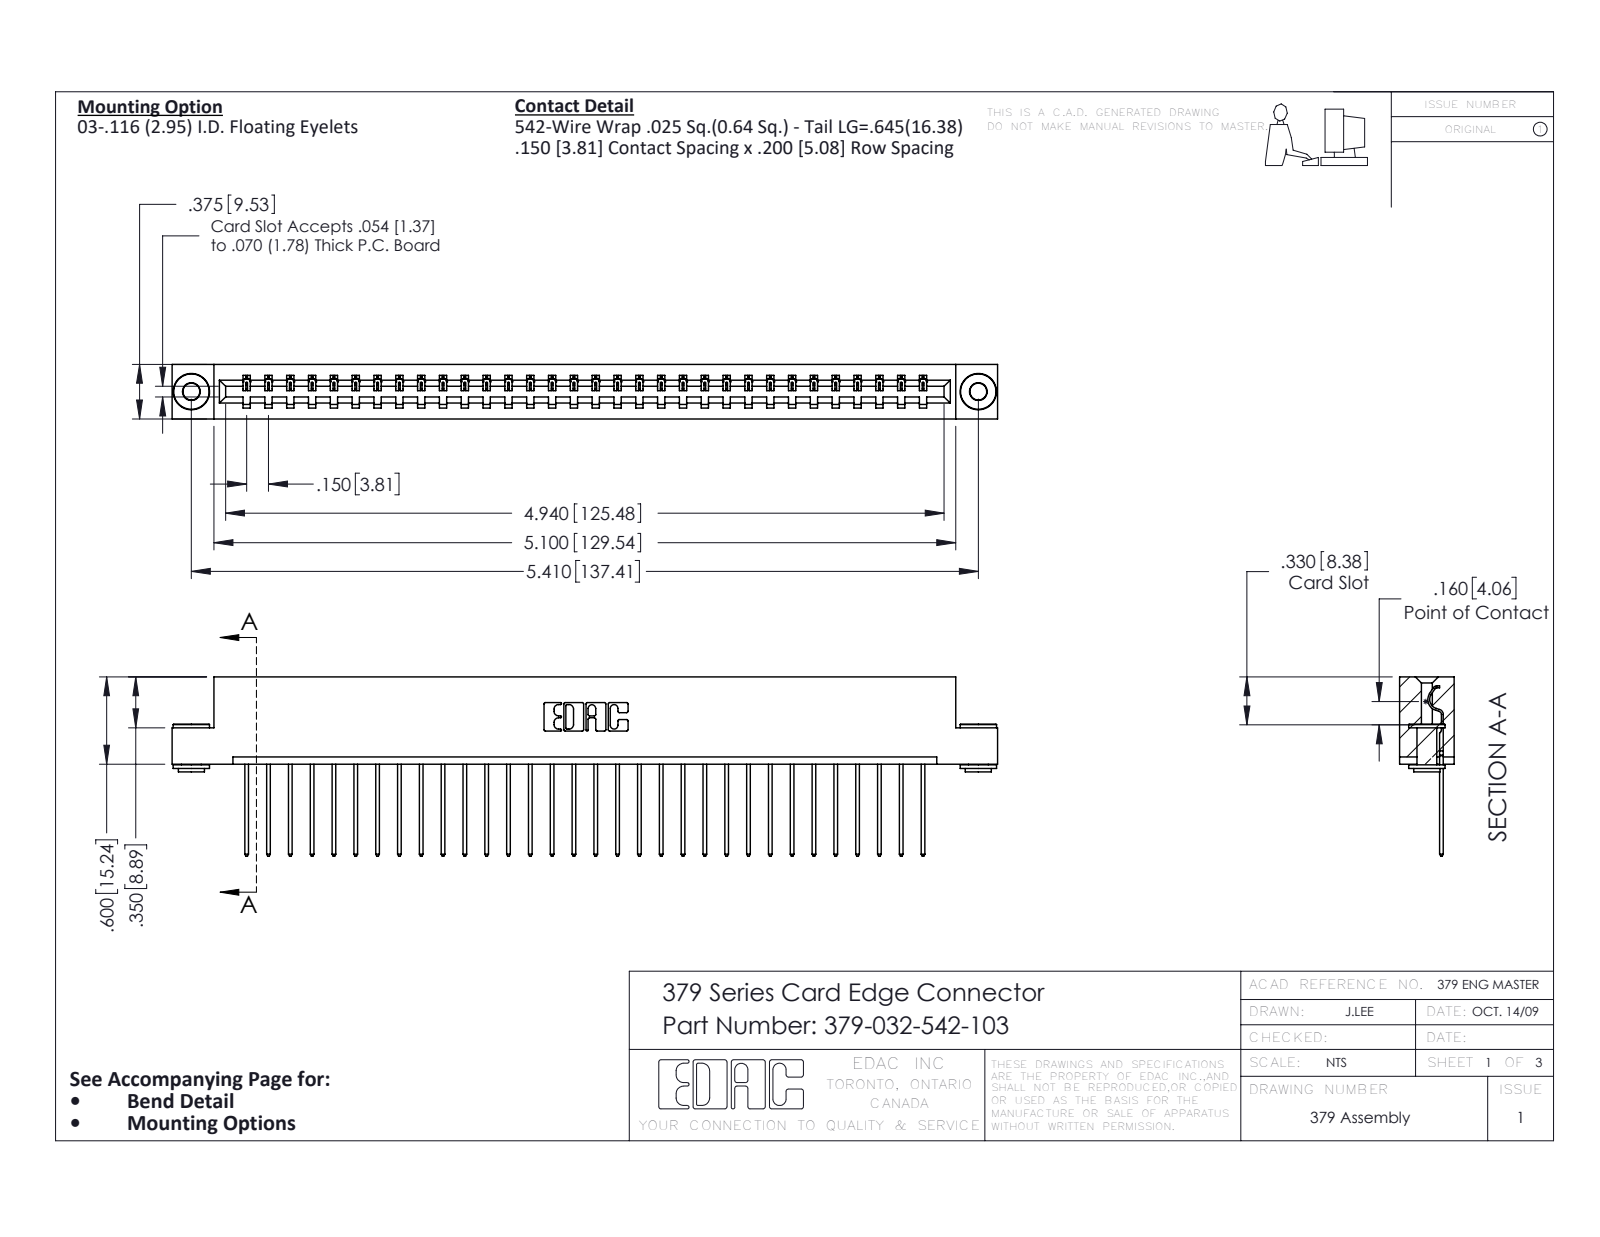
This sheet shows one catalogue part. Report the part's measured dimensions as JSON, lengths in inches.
{"part_name": "379 Part_Flush - .156 Dia - TH; 379-032-542-103; 345-250-002_345-250-002-102; 345-292-001_345-293-142", "step_written_by": "SolidWorks 2016 (CONFIG_CONTROL_DESIGN)", "units": "inches", "bodies": {"solids": 35, "faces": 2008, "planar": 1424, "cylindrical": 576, "other": 8}, "overall_size": [5.675, 1.232, 0.375], "volume_in3": 0.922, "surface_area_in2": 24.98, "round_holes": [[0.116, 2], [0.156, 2]], "round_bosses_or_shafts": [[0.25, 2], [0.18, 2], [0.136, 2]], "partial_cylinders_radius": [[0.006, 64], [0.01, 64], [0.01, 22], [0.007, 6], [0.031, 6], [0.026, 3], [0.014, 1], [0.022, 1]], "face_to_face_distances": [0.3, 0.075, 0.375, 0.225, 0.275, 0.025, 0.1, 0.2, 0.6, 0.55], "hole_center_spacings": [5.41]}
